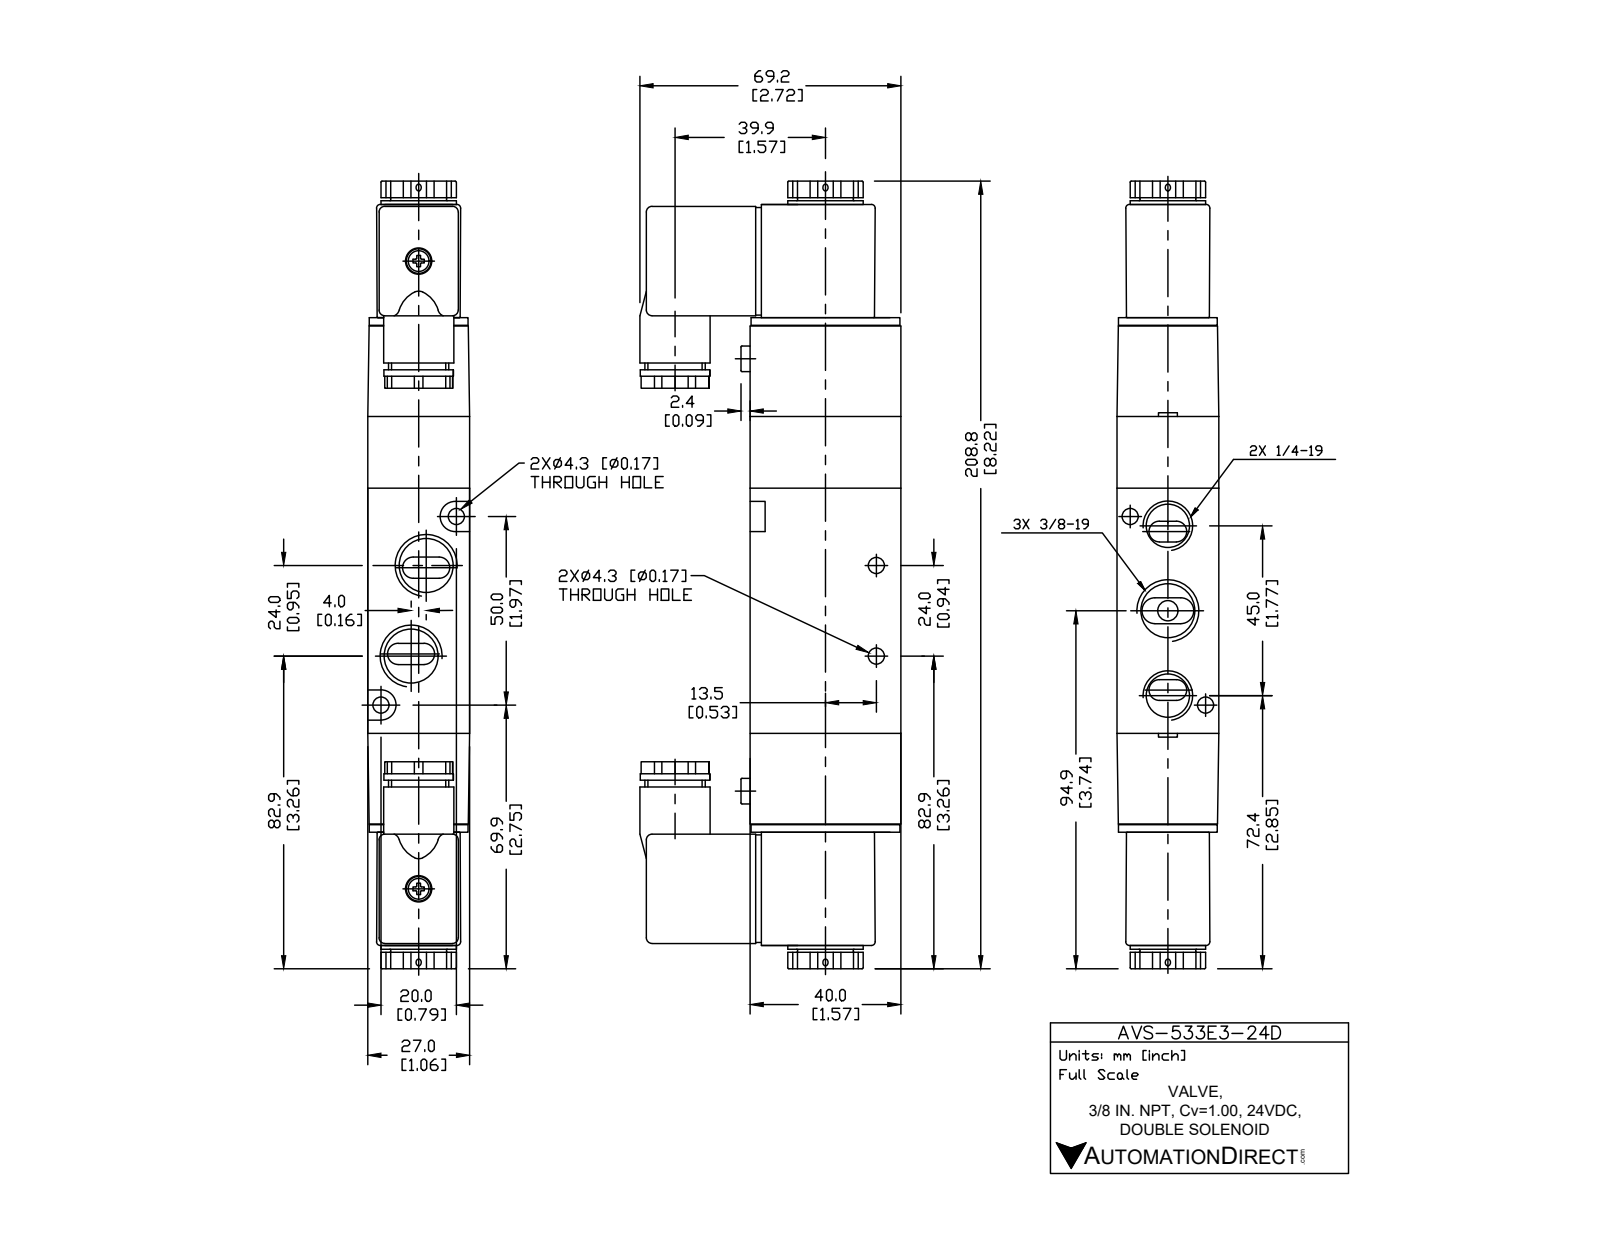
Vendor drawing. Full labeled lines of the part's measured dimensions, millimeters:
Part name (STEP PRODUCT): AVS-533E3-24D
STEP written by: SolidWorks 2015 (CONFIG_CONTROL_DESIGN)
Units: millimetres
Bodies: 5 solids, 272 faces (127 planar, 111 cylindrical, 34 other)
Overall size (bounding box): 208.8 × 69.2 × 27
Volume: 221 817 mm³ · Surface area: 45 967 mm²
Round holes (diameter × count): ⌀4.3 ×4, ⌀14.27 ×3, ⌀11.13 ×2, ⌀9.3 ×1
Round bosses / shafts (diameter × count): ⌀6.7 ×2, ⌀20 ×1, ⌀18.6 ×1, ⌀18.4 ×1, ⌀16 ×1, ⌀14.8 ×1
Partial cylindrical surfaces — rounded edges, fillets, slot ends (radius × count): R1.5 ×18, R3 ×12, R1 ×10, R0.5 ×8
Main face-to-face distances: 27, 3, 24, 40, 84, 23.22, 21, 29.5, 0.5, 166.4
Hole centre spacings: 10.31, 10.69, 12.17, 15.26, 22.5, 26.93, 34.56, 38.9
